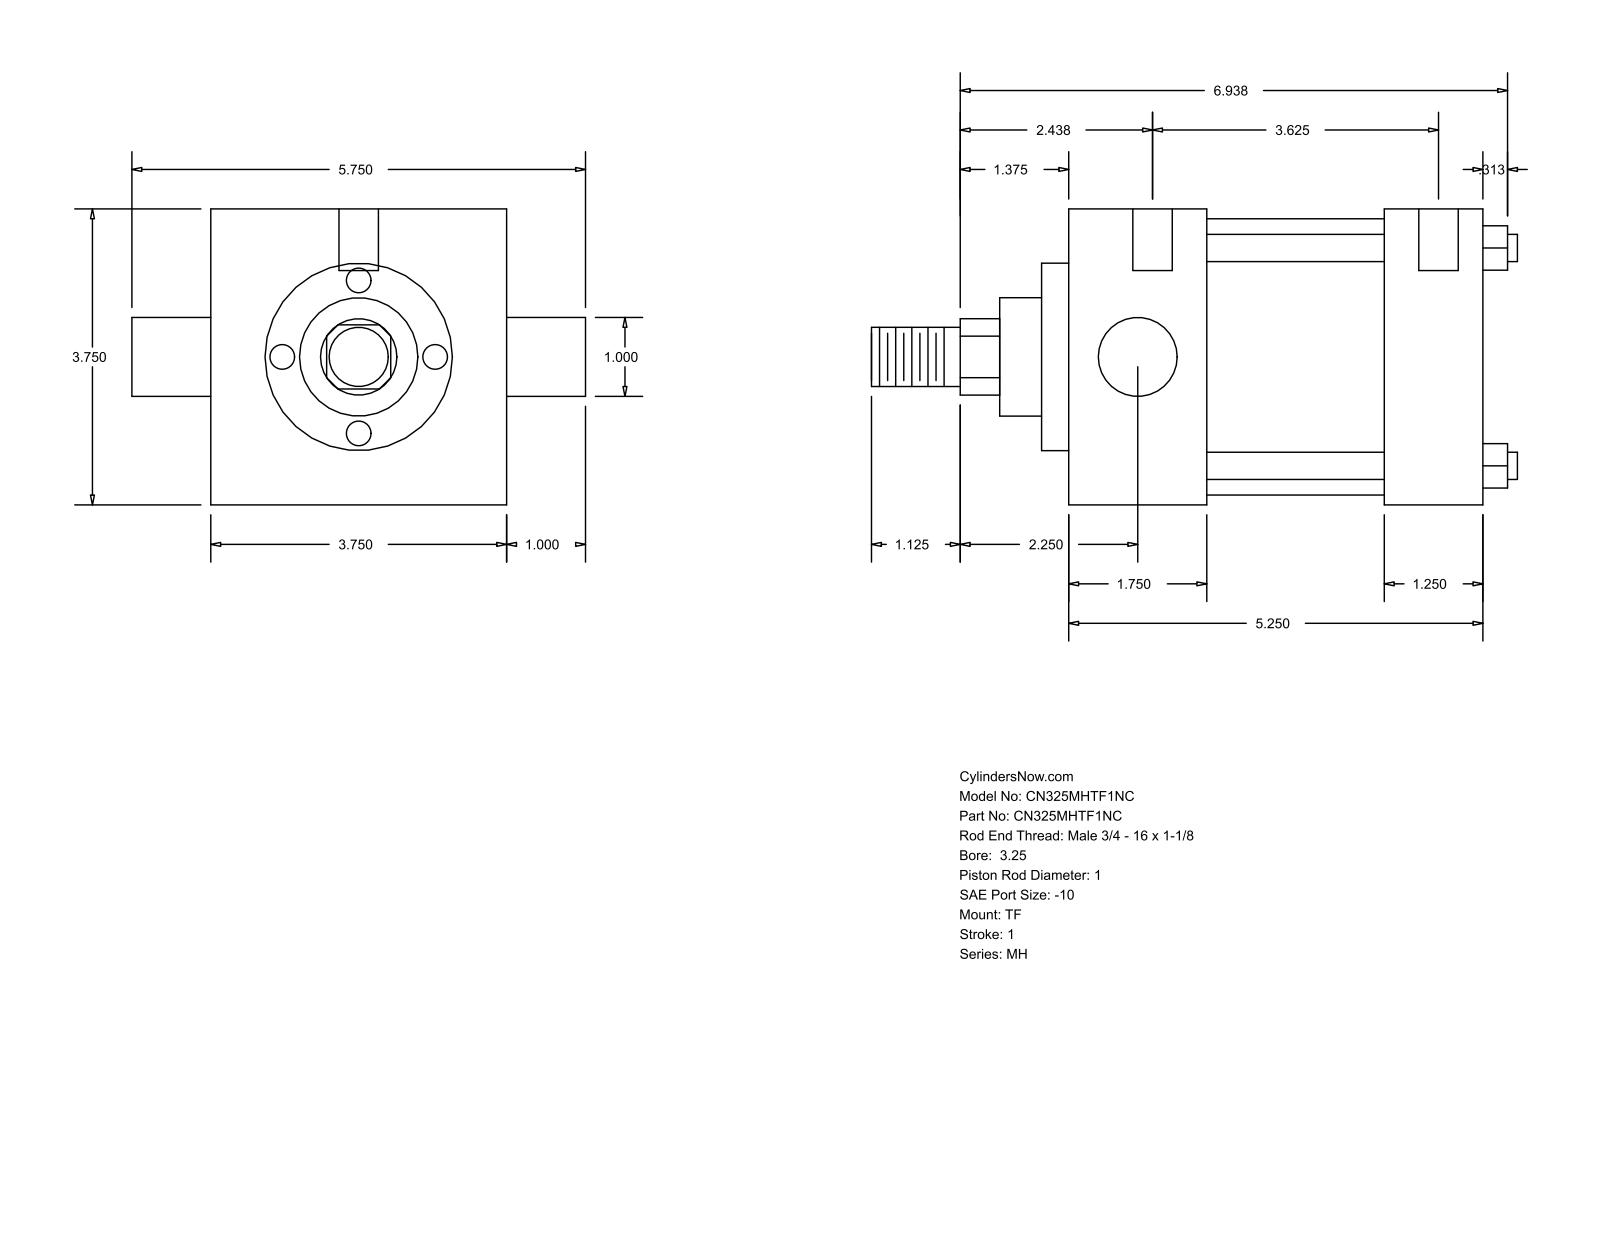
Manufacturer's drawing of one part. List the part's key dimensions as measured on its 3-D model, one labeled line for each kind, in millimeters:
Part name (STEP PRODUCT): MH_TF__0325_1
STEP written by: GSSL Pune (CONFIG_CONTROL_DESIGN)
Units: millimetres
Bodies: 0 solids, 86 faces (61 planar, 25 cylindrical, 0 other)
Overall size (bounding box): 207.96 × 146.05 × 95.25
Round holes (diameter × count): ⌀5.56 ×3, ⌀12.7 ×2
Round bosses / shafts (diameter × count): ⌀8.76 ×4, ⌀25.4 ×2, ⌀88.9 ×1, ⌀60.33 ×1, ⌀38.1 ×1, ⌀19.05 ×1
Partial cylindrical surfaces — rounded edges, fillets, slot ends (radius × count): R12.29 ×1
Main face-to-face distances: 95.24, 133.36, 44.46, 101.61, 57.15, 88.9, 31.75, 8.73, 53.19, 110.34
Hole centre spacings: 1.58, 4.76, 92.08, 93.66, 96.84, 98.42
